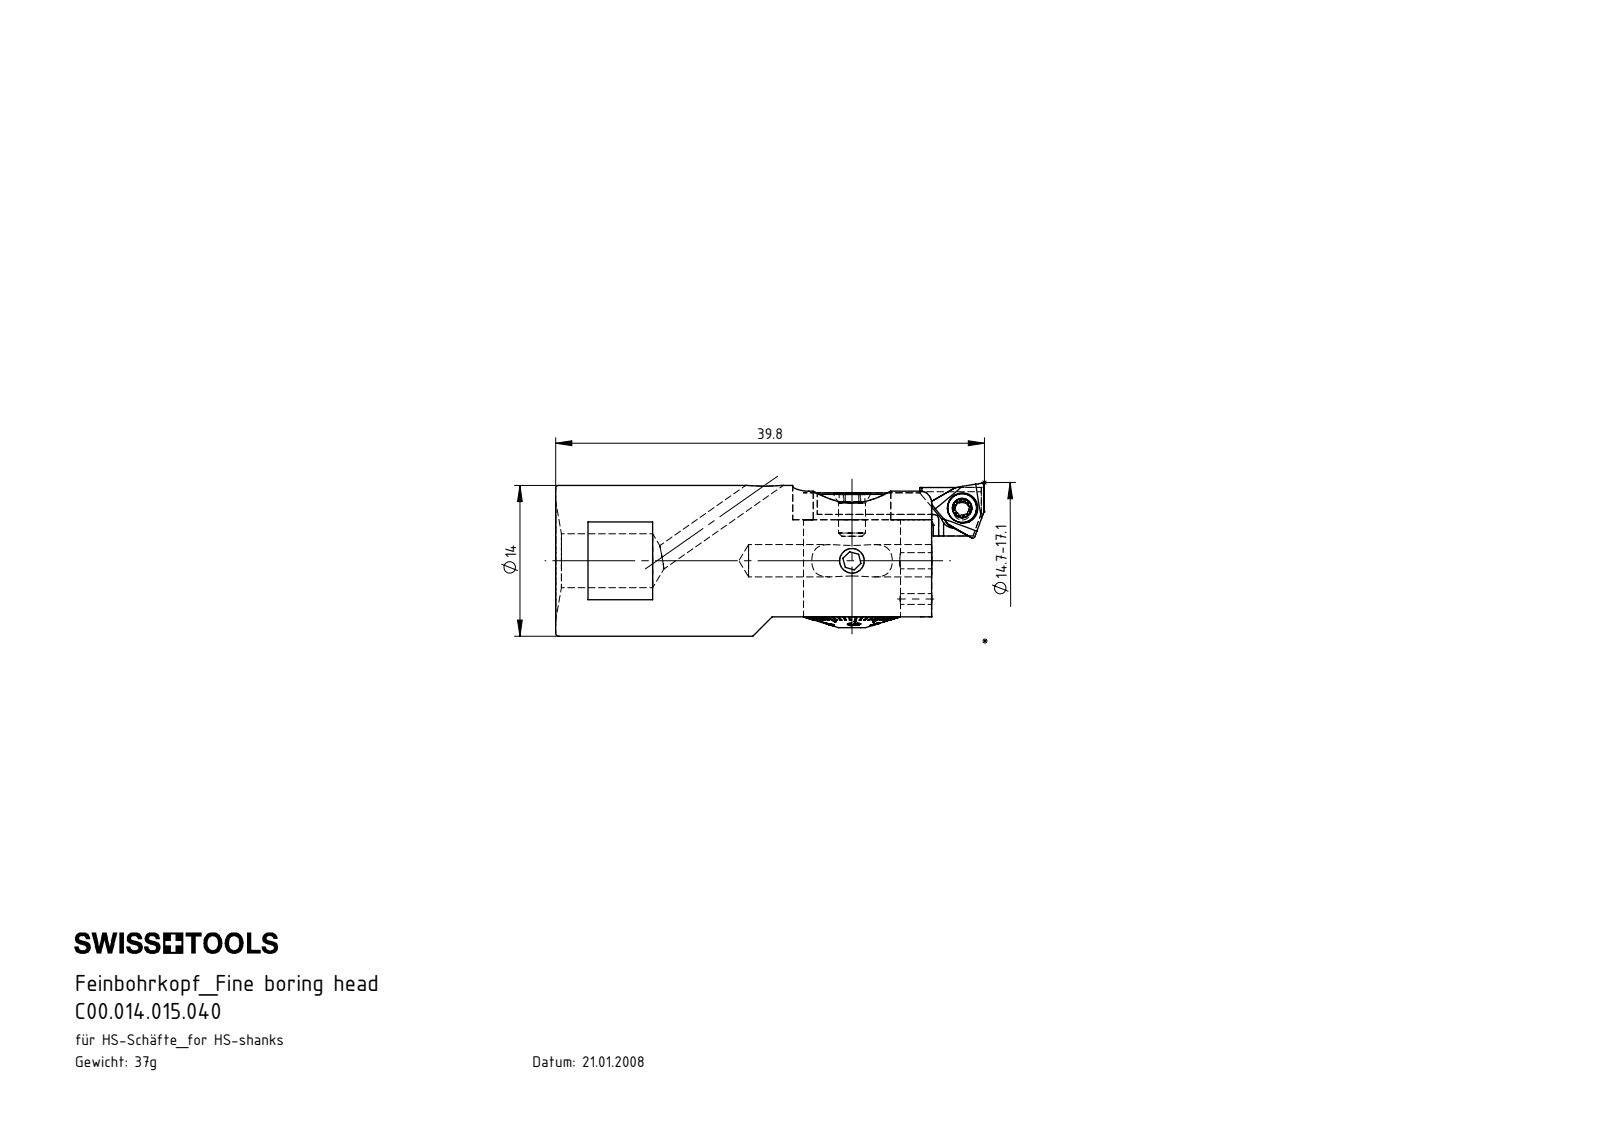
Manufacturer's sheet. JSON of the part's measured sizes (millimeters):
{"part_name": "DIN 3771 - 8x0.5; F14-WWA.001.004; F14-BG3.001.007_A; WWA-ER2.001.004_A (+8 more)", "step_written_by": "SolidWorks 2017 (AUTOMOTIVE_DESIGN)", "units": "millimeters", "bodies": {"solids": 13, "faces": 564, "planar": 397, "cylindrical": 78, "other": 89}, "overall_size": [39.76, 14.21, 14], "volume_mm3": 4756, "surface_area_mm2": 3932, "round_holes": [[2, 2], [2.3, 2], [1, 1], [1.5, 1], [1.6, 1], [2.7, 1], [3, 1], [3.25, 1], [5, 1], [6.05, 1], [6.2, 1]], "round_bosses_or_shafts": [[3, 2], [14, 1], [9, 1], [7.85, 1], [5.9, 1], [5.85, 1], [5.6, 1], [3.95, 1]], "partial_cylinders_radius": [[0.3, 9], [0.21, 6], [0.24, 6], [0.45, 6], [0.7, 2], [1, 2], [1.25, 2], [1.5, 2]], "face_to_face_distances": [2.5, 9, 6.5, 3.3, 8.7, 2.1, 0.4, 8.6, 4, 5], "hole_center_spacings": [0.65, 3.55, 4, 5.35]}
